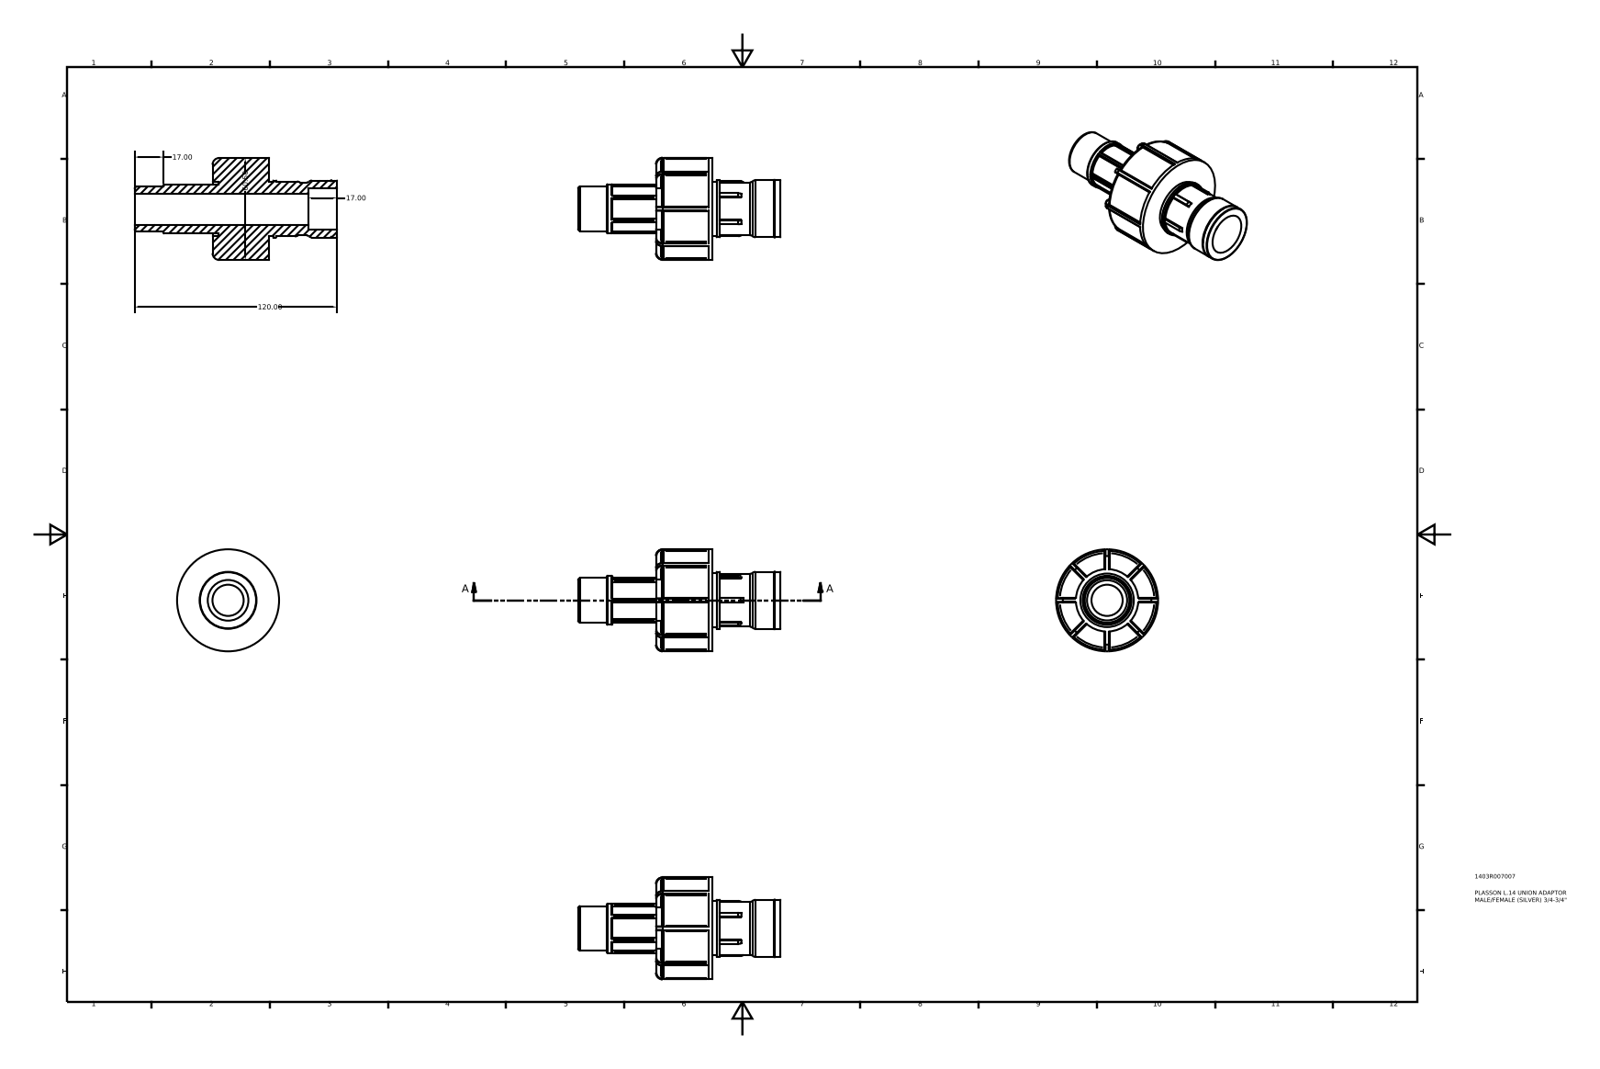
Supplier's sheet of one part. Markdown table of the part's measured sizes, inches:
| quantity | value |
| --- | --- |
| part name | 1403R007007 |
| STEP written by | Autodesk Inventor 2015 (AUTOMOTIVE_DESIGN) |
| units | inches |
| bodies | 1 solid, 267 faces (77 planar, 126 cylindrical, 64 other) |
| overall size | 4.724 × 2.382 × 2.382 |
| volume | 6.728 in³ |
| surface area | 44.43 in² |
| round holes (diameter × count) | 0.729 × 1, 0.95 × 1, 1.249 × 1 |
| round bosses / shafts (diameter × count) | 2.382 × 1, 2.311 × 1, 1.457 × 1, 1.329 × 1, 1.263 × 1, 1.234 × 1, 1.145 × 1, 1.041 × 1 |
| partial cylindrical surfaces (radius × count) | 0.012 × 52, 0.009 × 12, 0.021 × 12, 0.119 × 5 |
| main face-to-face distances | 1.189, 0.134, 2.772, 1.583, 1.323, 2.906, 0.095, 0.669, 4.055, 0.094 |
